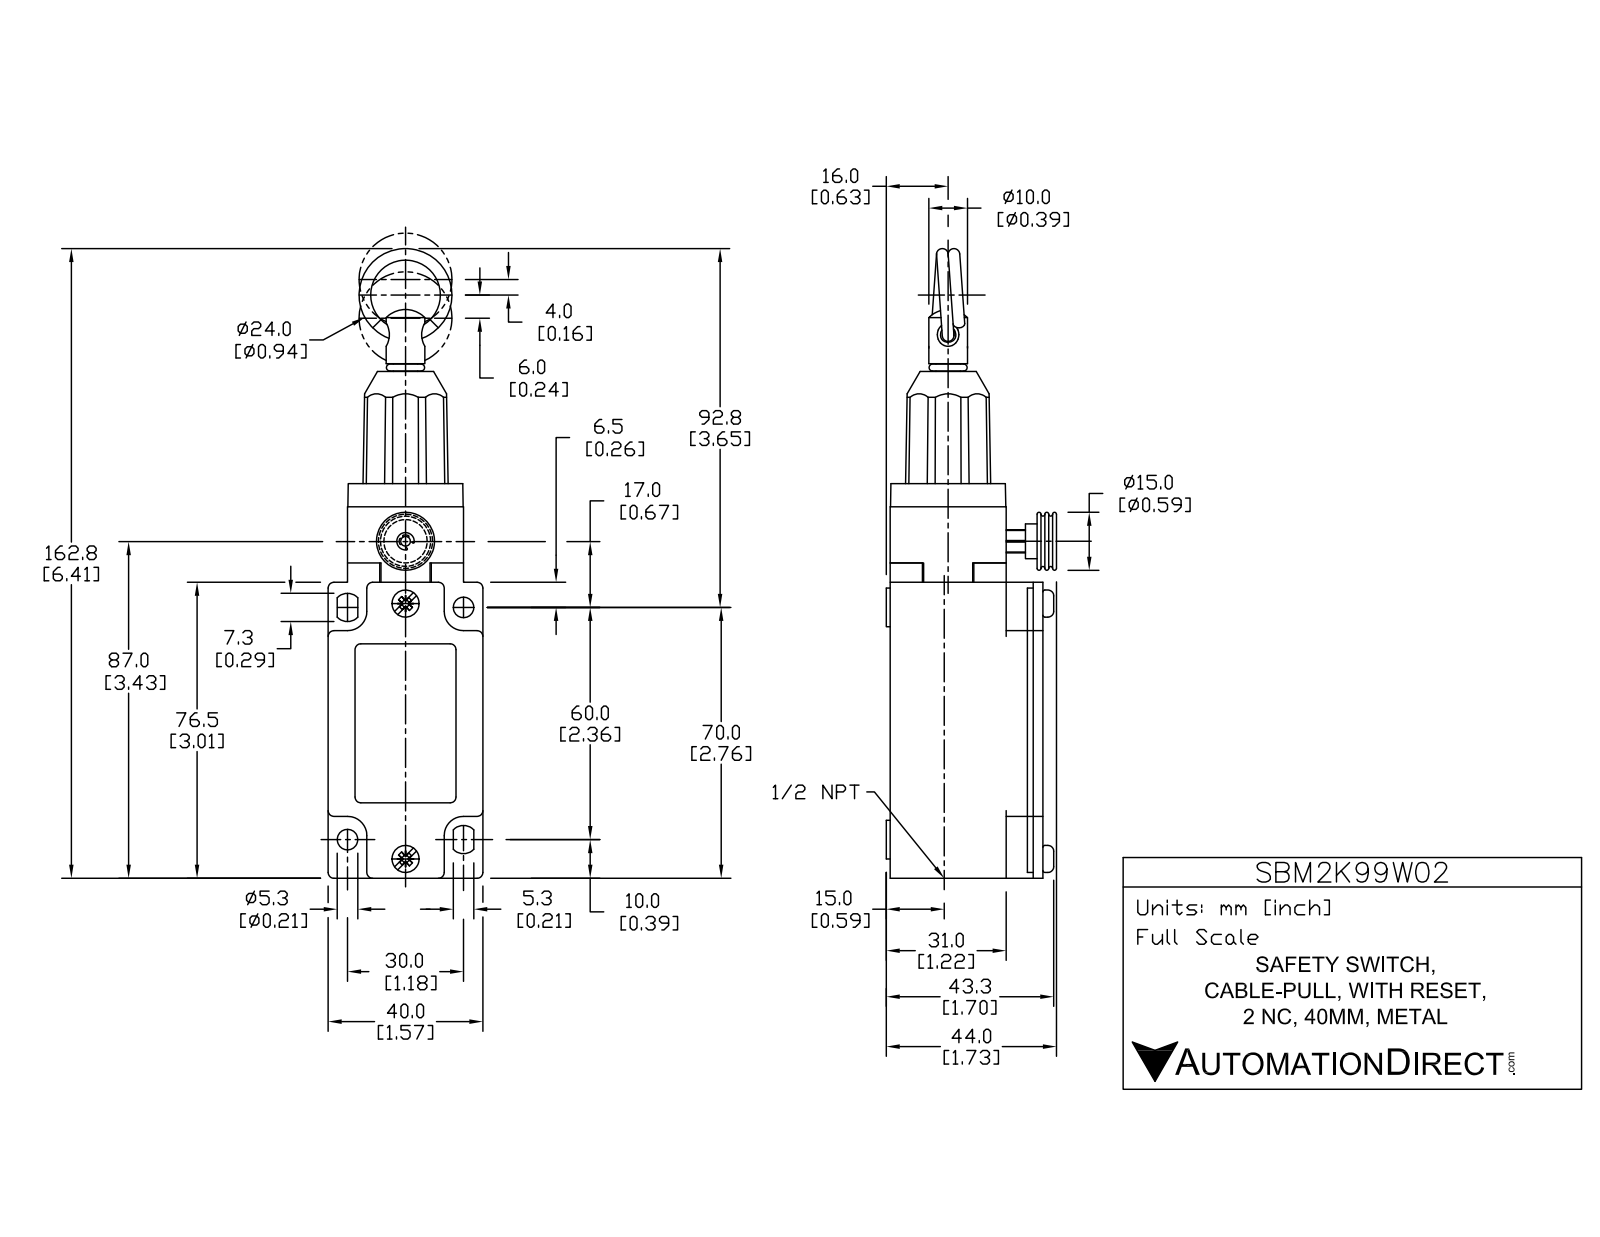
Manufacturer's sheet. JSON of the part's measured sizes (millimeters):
{"part_name": "SBM2K99W02", "step_written_by": "SolidWorks 2017 (AUTOMOTIVE_DESIGN)", "units": "millimeters", "bodies": {"solids": 5, "faces": 233, "planar": 91, "cylindrical": 88, "other": 54}, "overall_size": [164, 43.8, 40], "volume_mm3": 142500, "surface_area_mm2": 30610, "round_holes": [[5.2, 2], [4, 1], [10.1, 1], [17, 1], [18, 1], [19, 1]], "round_bosses_or_shafts": [[10, 5], [7, 2], [17.8, 1], [9.8, 1], [6.7, 1], [6.3, 1], [2.5, 1]], "partial_cylinders_radius": [[1.5, 16], [5, 4], [3.3, 2], [11.5, 1], [12, 1]], "face_to_face_distances": [40, 5, 30, 39.5, 35, 9.5, 76.5, 1, 26, 25], "hole_center_spacings": [1, 67.1]}
